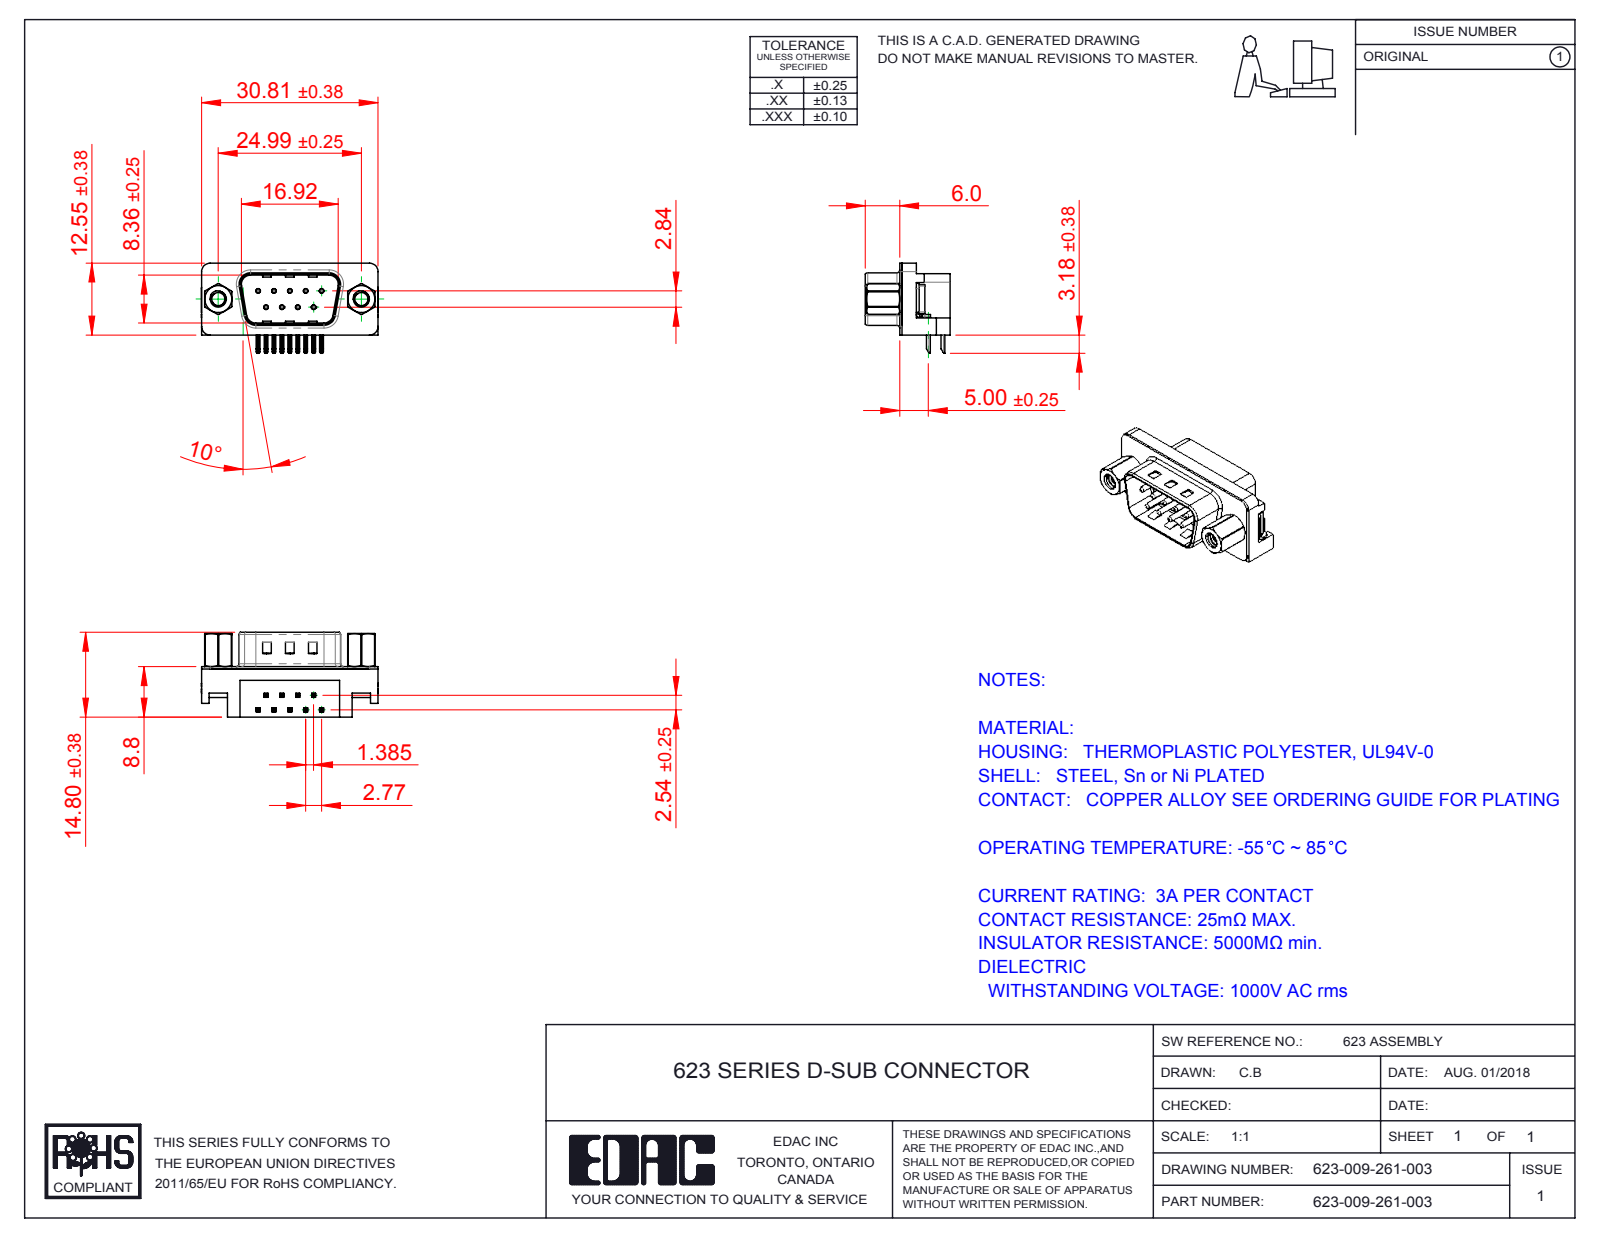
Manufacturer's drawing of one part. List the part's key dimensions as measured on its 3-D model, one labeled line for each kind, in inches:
Part name (STEP PRODUCT): 623 Contact Bottom; 623 Shell_9 Socket; 623 Housing_9 Socket; 623 Contact Top (+4 more)
STEP written by: SolidWorks 2016 (CONFIG_CONTROL_DESIGN)
Units: inches
Bodies: 17 solids, 1105 faces (595 planar, 373 cylindrical, 137 other)
Overall size (bounding box): 1.216 × 0.619 × 0.583
Volume: 0.163 in³ · Surface area: 6.581 in²
Round holes (diameter × count): ⌀0.014 ×9, ⌀0.031 ×9, ⌀0.089 ×2, ⌀0.09 ×2, ⌀0.157 ×2, ⌀0.189 ×2, ⌀0.197 ×2
Round bosses / shafts (diameter × count): ⌀0.03 ×9, ⌀0.193 ×2, ⌀0.187 ×2, ⌀0.154 ×2, ⌀0.11 ×2
Partial cylindrical surfaces — rounded edges, fillets, slot ends (radius × count): R0.01 ×44, R0.005 ×18, R0.039 ×16, R0.02 ×9, R0.059 ×8, R0.035 ×4, R0.063 ×4, R0.079 ×4
Main face-to-face distances: 0.016, 0.331, 0.346, 0.232, 0.114, 0.098, 0.014, 0.345, 0.421, 0.407
Hole centre spacings: 0.124, 0.109, 0.218, 0.198, 0.198, 0.327, 0.294, 0.295
